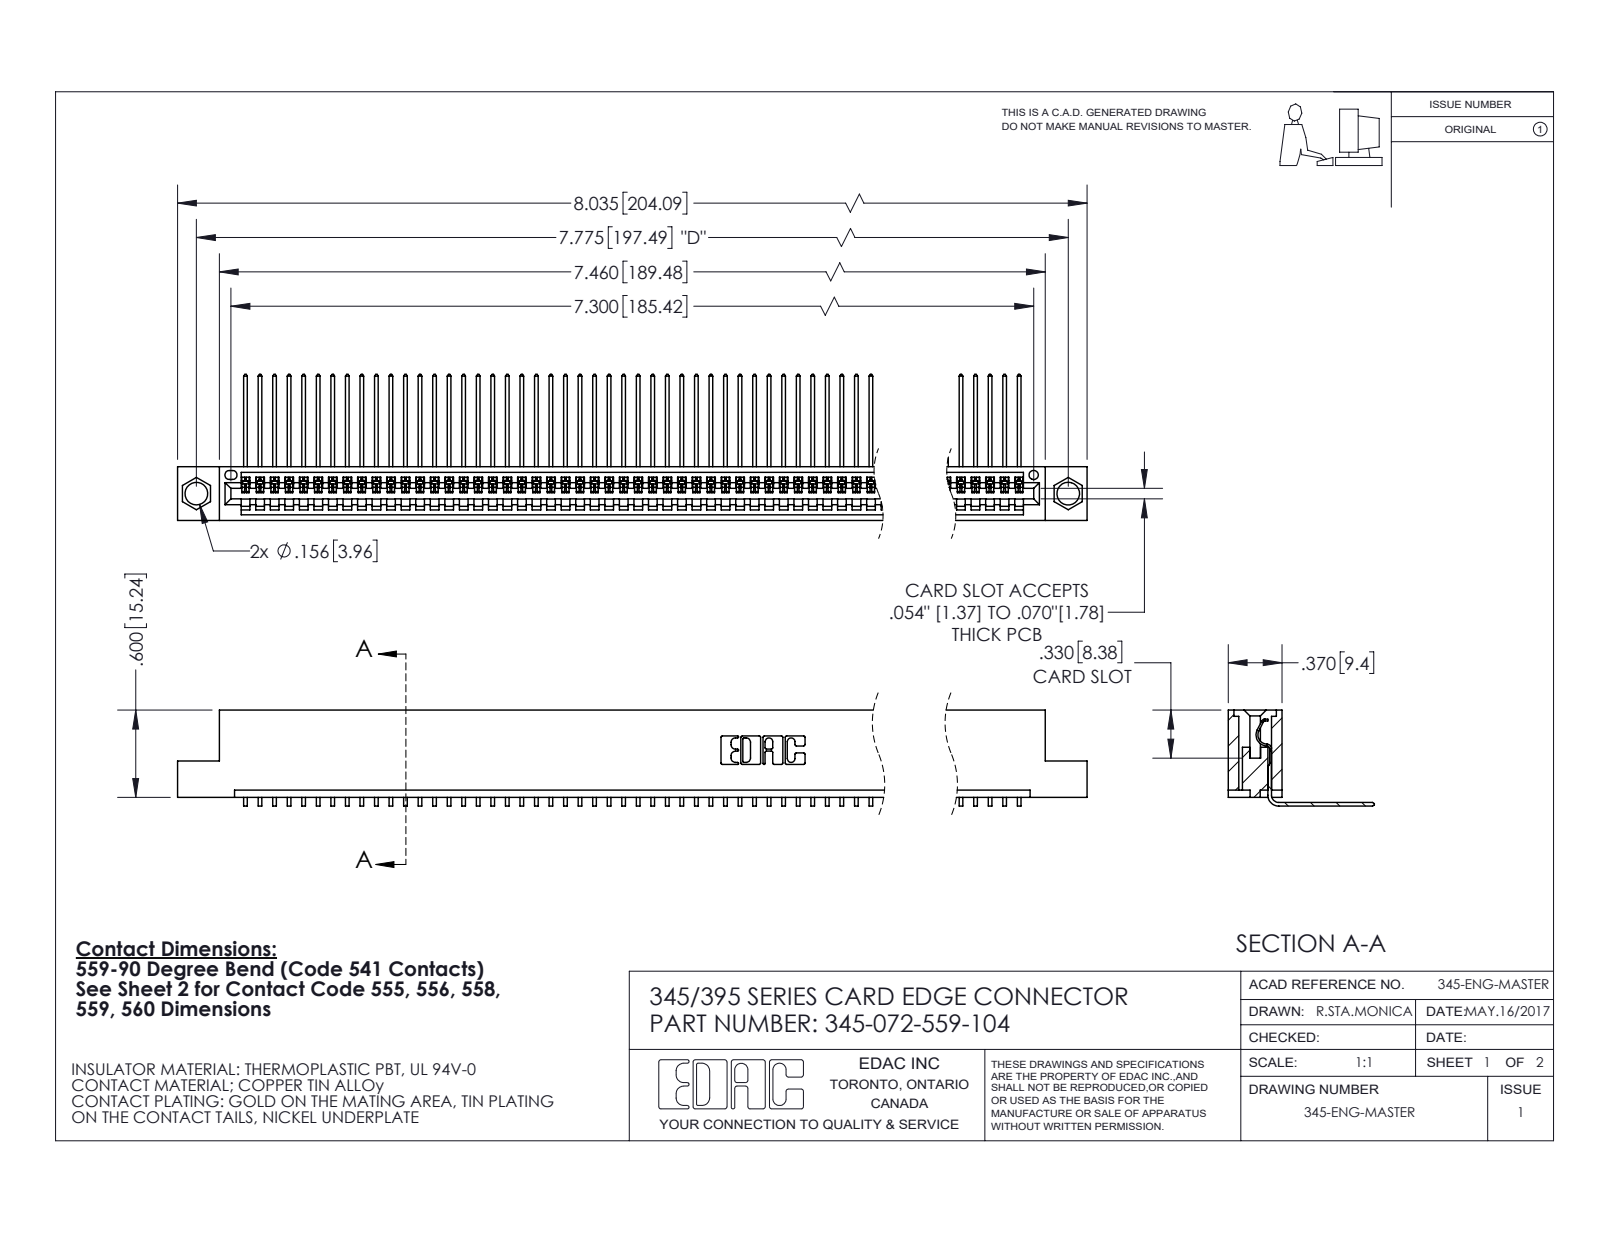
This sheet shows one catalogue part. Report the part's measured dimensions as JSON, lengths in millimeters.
{"part_name": "345-292-001_558 559 Tail - 1; 345 Part_Flush Mounting Lugs - 0.156 Dia-TI; 345-072-559-104", "step_written_by": "SolidWorks 2020 (CONFIG_CONTROL_DESIGN)", "units": "millimeters", "bodies": {"solids": 73, "faces": 4460, "planar": 3118, "cylindrical": 1342, "other": 0}, "overall_size": [204.1, 25.5, 16.7], "volume_mm3": 19760, "surface_area_mm2": 27920, "round_holes": [[4, 2], [1.6, 1]], "partial_cylinders_radius": [[0.2, 144], [0.3, 22], [0.2, 6], [0.8, 6], [0.7, 3], [0.8, 2], [1, 2], [0.4, 1]], "face_to_face_distances": [1.8, 7.6, 9.4, 5.1, 2.5, 6.9, 0.6, 5.7, 3.8, 1.8], "hole_center_spacings": [6.9, 191.5, 197.5]}
